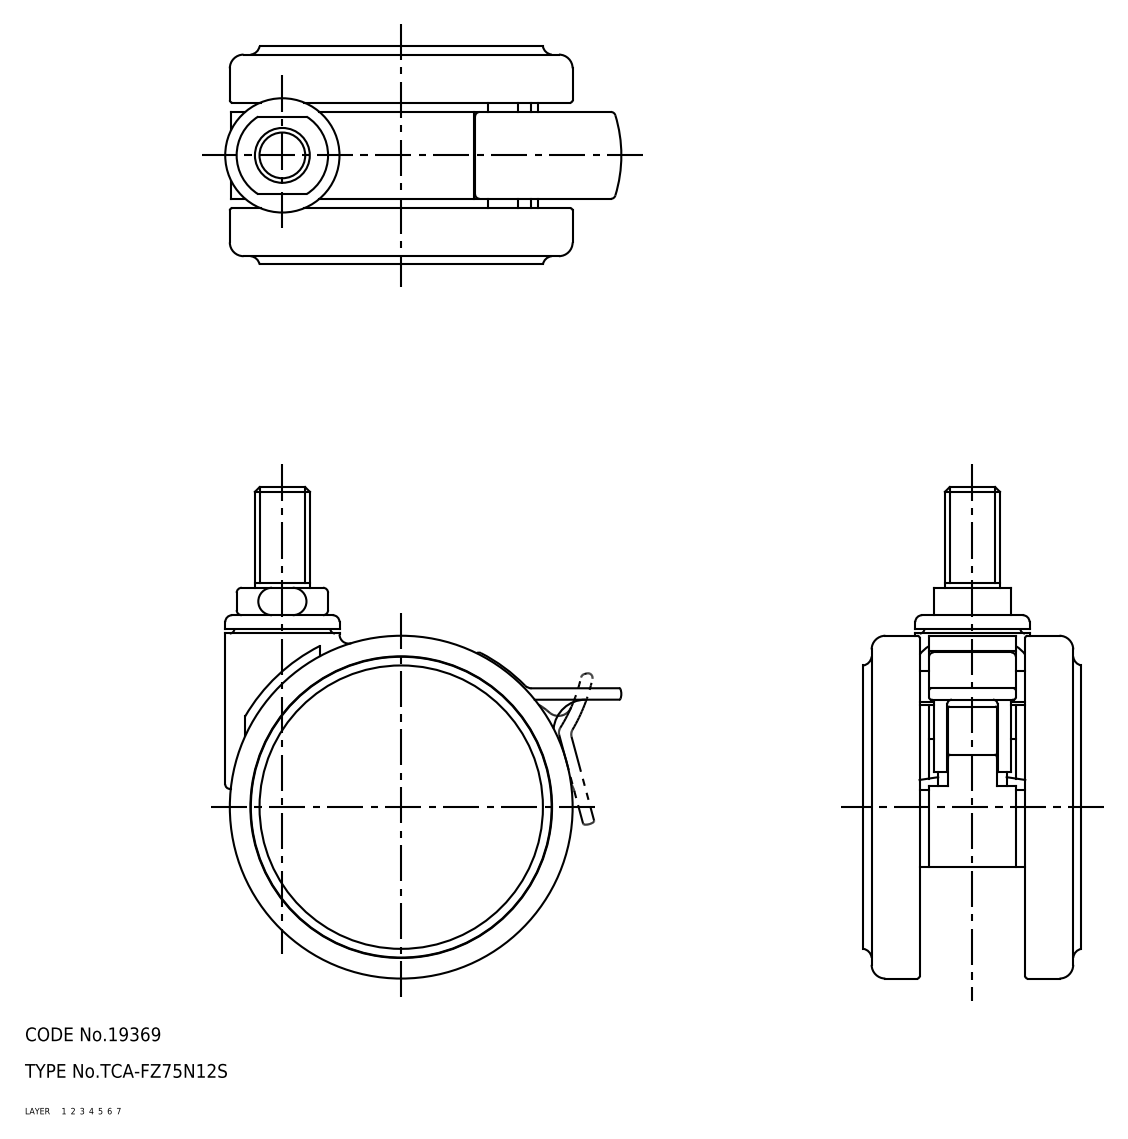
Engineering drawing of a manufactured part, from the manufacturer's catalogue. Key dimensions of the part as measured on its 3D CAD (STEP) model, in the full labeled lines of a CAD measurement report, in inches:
Part name (STEP PRODUCT): caster; TCA-FZ75N12S
STEP written by: SolidWorks 2015 (AUTOMOTIVE_DESIGN)
Units: inches
Bodies: 1 solid, 2254 faces (508 planar, 984 cylindrical, 762 other)
Overall size (bounding box): 4.232 × 3.412 × 1.878
Volume: 7.327 in³ · Surface area: 110.6 in²
Round holes (diameter × count): ⌀0.094 ×1, ⌀0.142 ×1, ⌀0.228 ×1, ⌀0.256 ×1, ⌀0.315 ×1, ⌀0.319 ×1, ⌀0.335 ×1, ⌀0.354 ×1, ⌀0.402 ×1, ⌀0.433 ×1, ⌀0.638 ×1, ⌀0.669 ×1
Round bosses / shafts (diameter × count): ⌀0.63 ×2, ⌀2.591 ×1, ⌀2.126 ×1, ⌀1.024 ×1, ⌀0.984 ×1, ⌀0.551 ×1, ⌀0.472 ×1, ⌀0.394 ×1
Partial cylindrical surfaces — rounded edges, fillets, slot ends (radius × count): R0.039 ×176, R0.02 ×157, R0.012 ×142, R0.008 ×18, R0.079 ×13, R0.059 ×7, R0.028 ×2, R0.031 ×2
Main face-to-face distances: 0.059, 1.819, 0.071, 0.13, 1.748, 1.689, 1.264, 0.354, 0.484, 1.394
Hole centre spacings: 1.181
